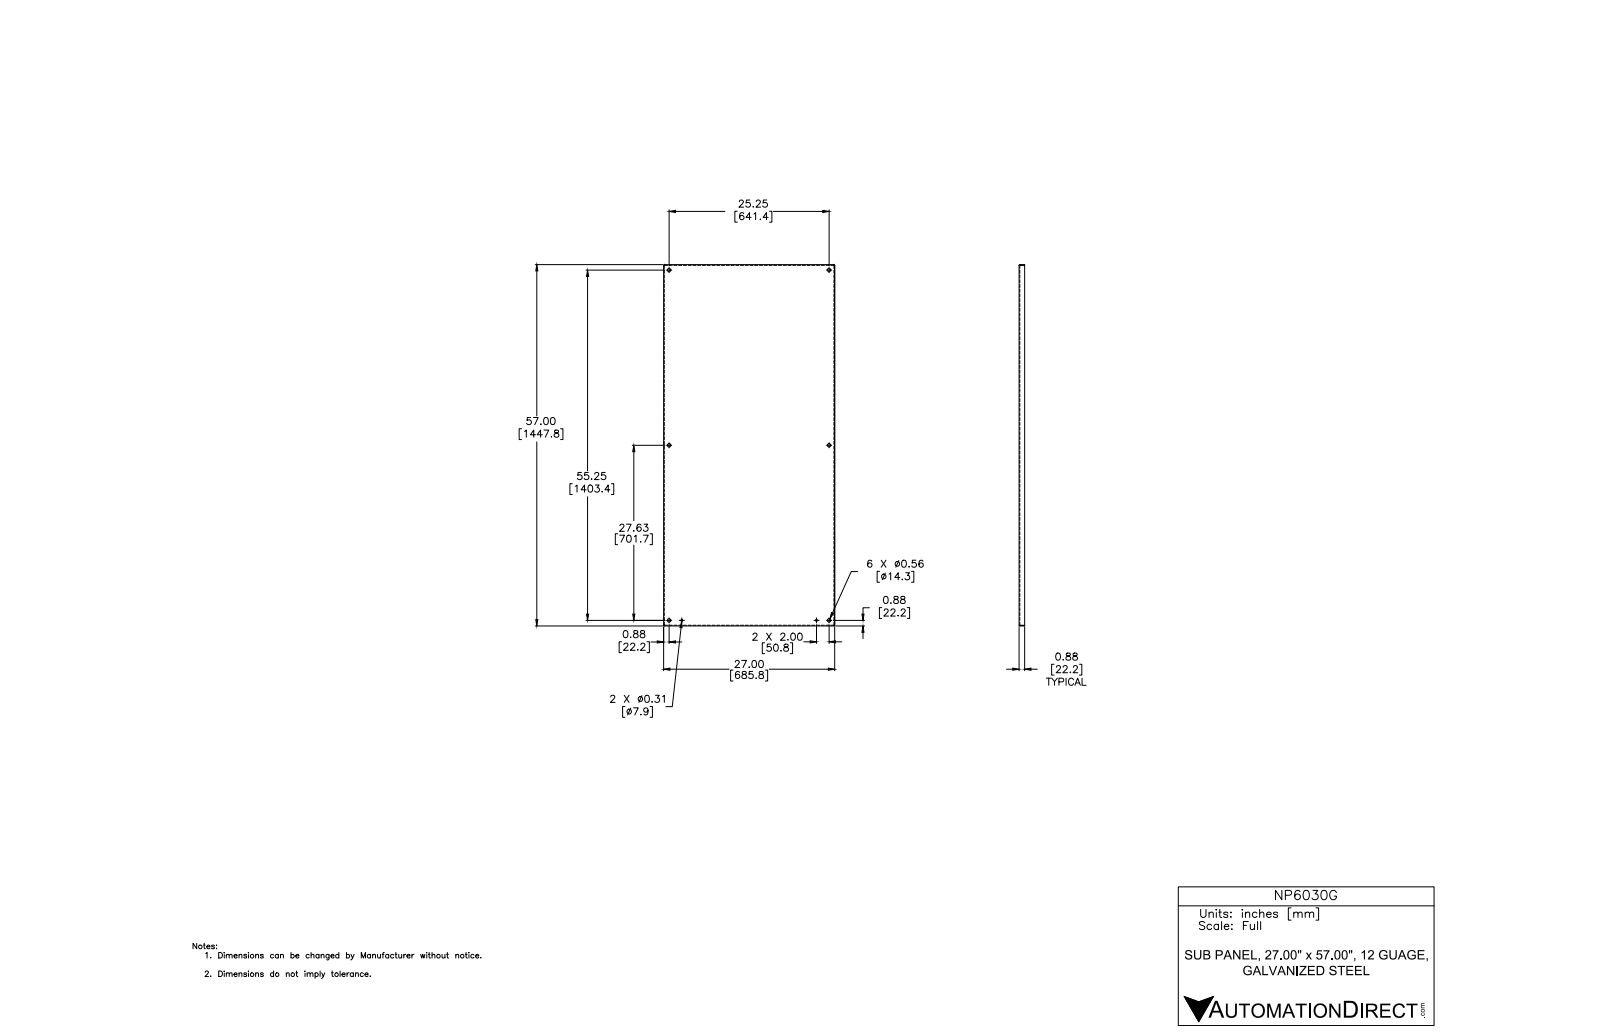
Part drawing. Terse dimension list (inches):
name: NP6030G
written by: Autodesk Inventor 2012 (AUTOMOTIVE_DESIGN)
unit: in
bodies: 1 solid, 46 faces (22 planar, 16 cylindrical, 8 other)
size: 57 × 27 × 0.875
volume: 155.8 in³; area: 3 342 in²
holes: 6× ⌀0.563, 2× ⌀0.312
rounds: 4× R0.031, 4× R0.125
face distances: 0.094, 26.906, 27, 26.813, 56.906, 57, 56.813, 0.781, 0.875, 0.105
hole spacings: 27.625, 37.426, 25.25, 27.697, 36.107, 55.286, 59.942, 2
